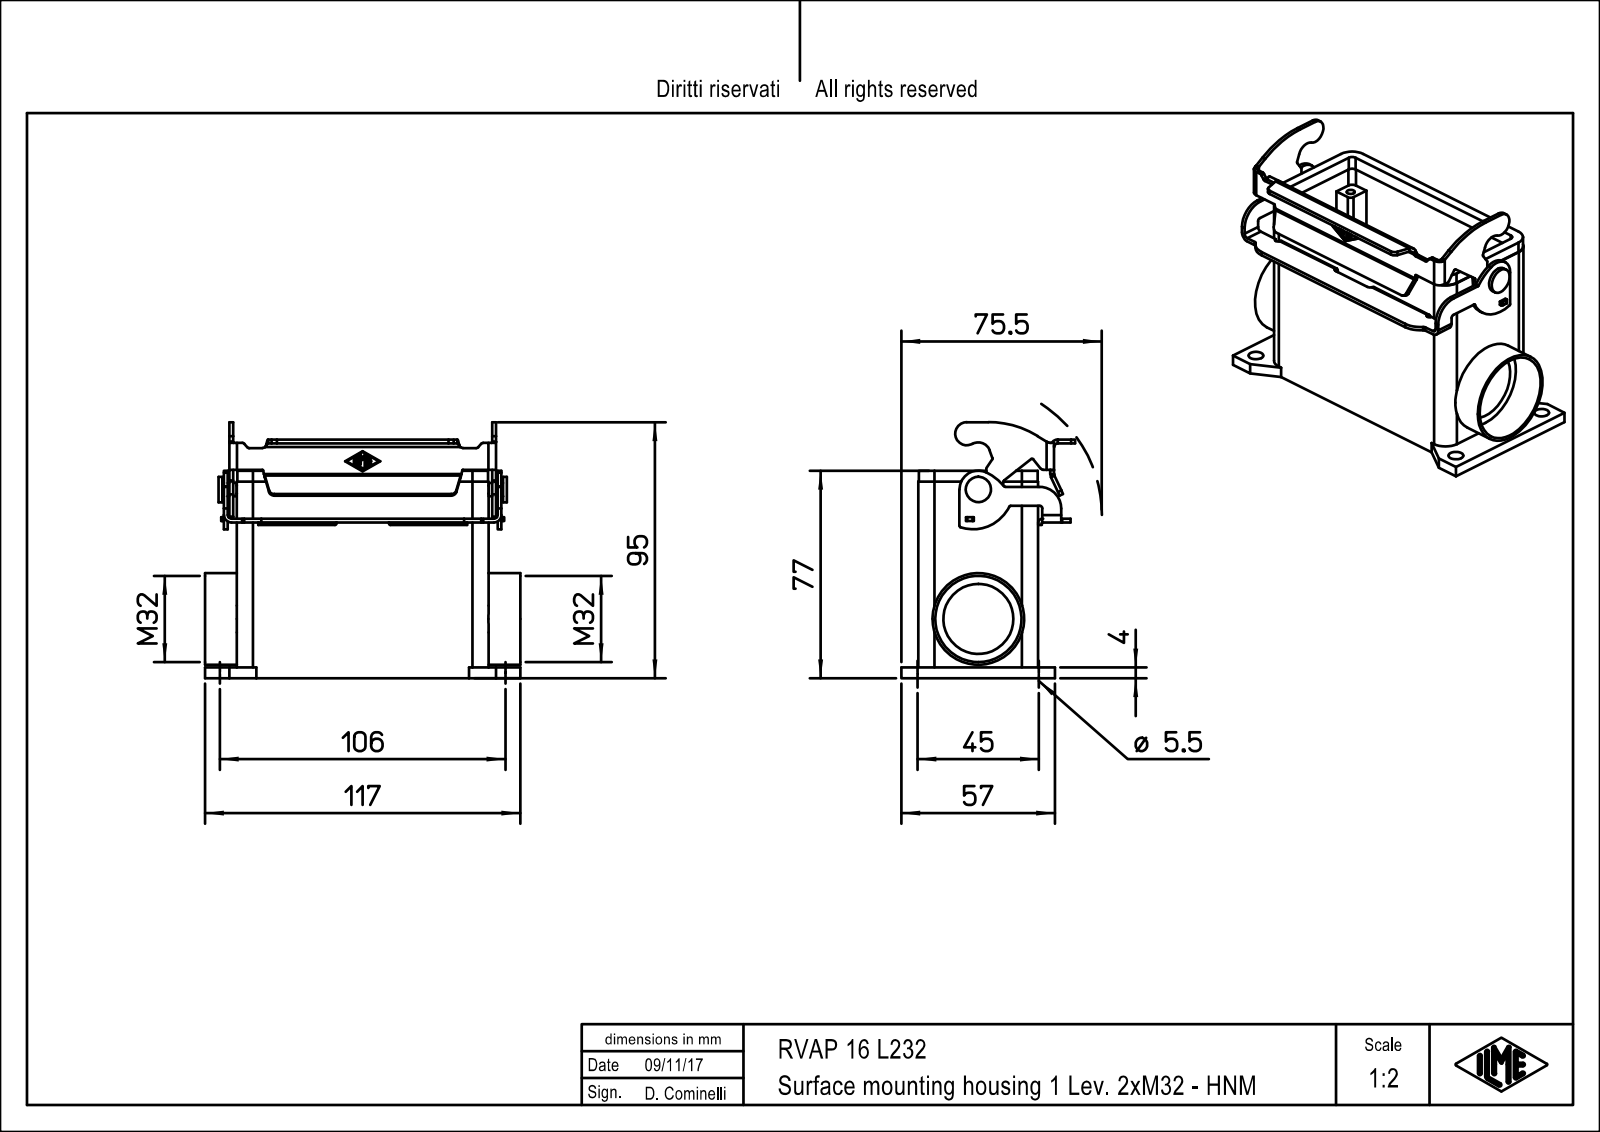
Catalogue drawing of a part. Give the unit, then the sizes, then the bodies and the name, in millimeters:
Units: millimetres
Overall size (bounding box): 117 × 95 × 64.48
Round holes (diameter × count): ⌀2.46 ×4, ⌀3 ×4, ⌀5.5 ×4, ⌀26 ×1, ⌀32 ×1
Round bosses / shafts (diameter × count): ⌀34 ×1, ⌀9.4 ×1, ⌀5 ×1, ⌀3 ×1
Partial cylindrical surfaces — rounded edges, fillets, slot ends (radius × count): R0.25 ×16, R0.5 ×12, R1 ×12, R1.5 ×11, R2 ×8, R1.4 ×6, R2.8 ×6, R1.8 ×4
Main face-to-face distances: 4, 40.5, 44.5, 36.5, 1.4, 11.5, 82, 2, 99.6, 6.75
Hole centre spacings: 16.43, 38.54, 91.69, 98.09, 27, 45, 77.5, 82.07
Volume: 120 173 mm³ · Surface area: 67 396 mm²
Bodies: 1 solid, 383 faces (201 planar, 170 cylindrical, 12 other)
Part name (STEP PRODUCT): RVAP_16_L232
STEP written by: PTC Creo Elements/Direct Modeling 19.0E 27-Jun-2016 (C) Parametric Technology GmbH (AUTOMOTIVE_DESIGN)
